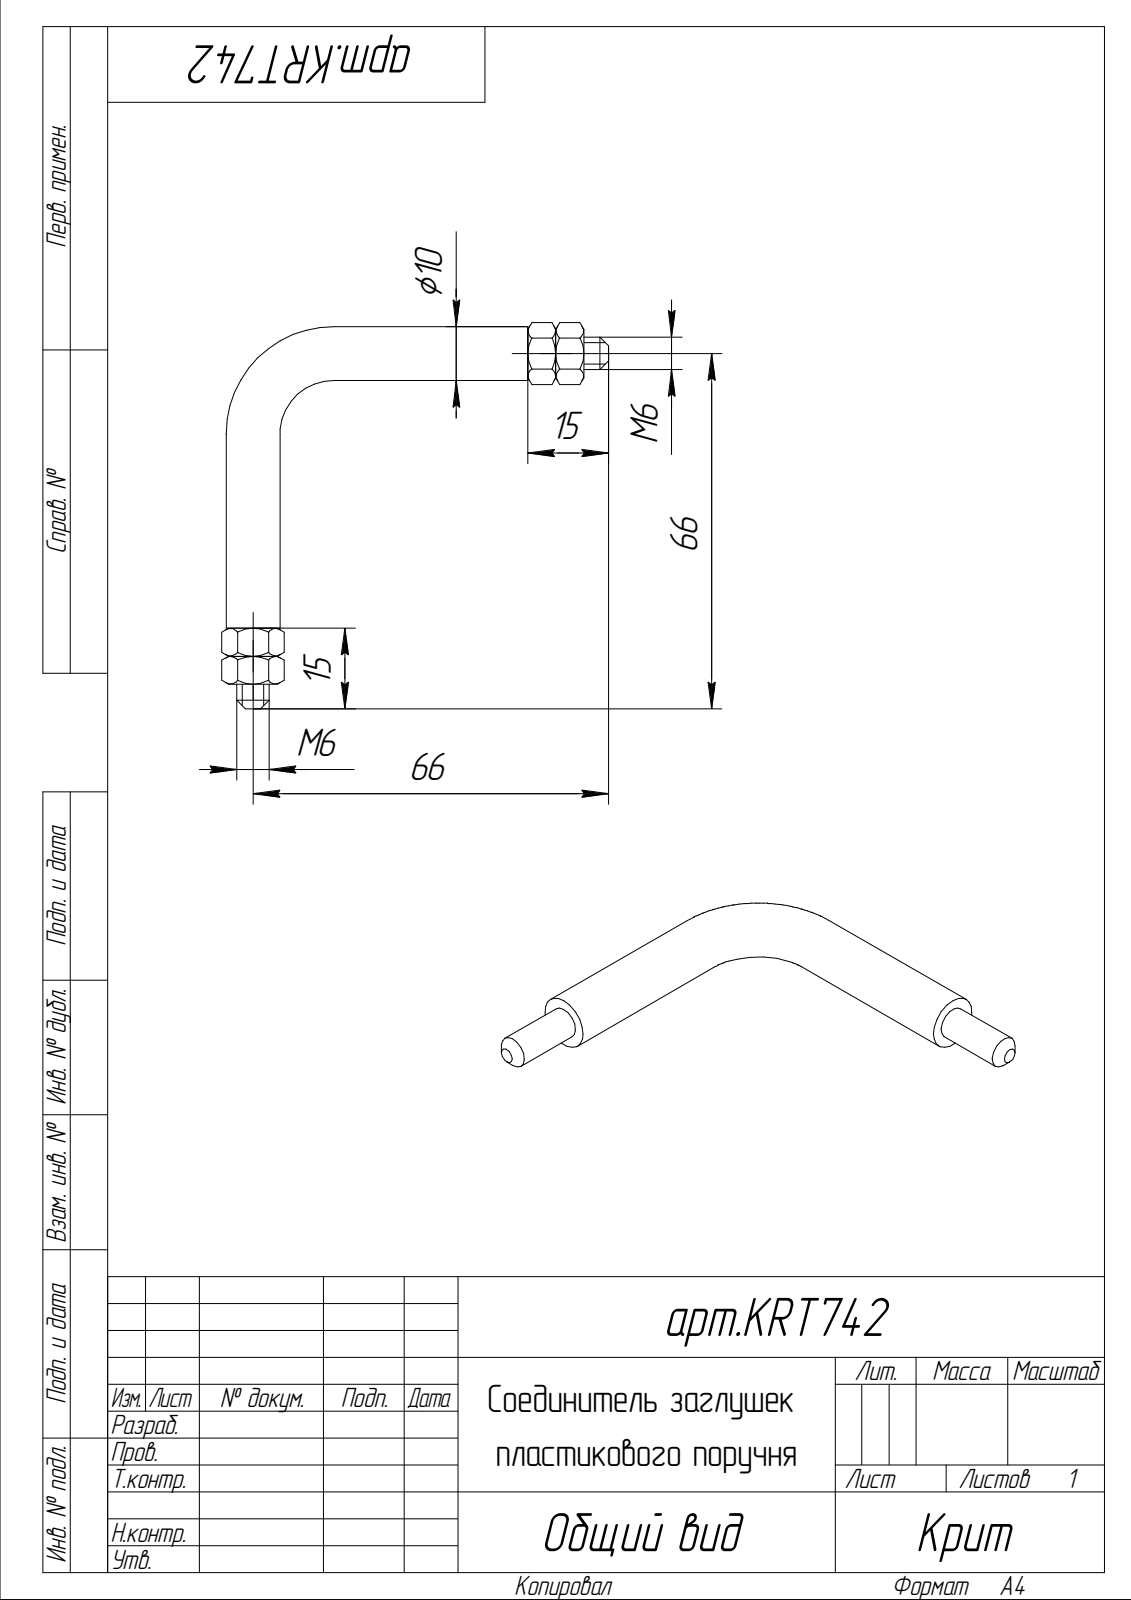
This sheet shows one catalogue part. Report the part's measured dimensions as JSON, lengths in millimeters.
{"part_name": "Соединитель заглушек пластикового поручня", "step_written_by": "ASCON Math Kernel (AUTOMOTIVE_DESIGN)", "units": "millimeters", "bodies": {"solids": 1, "faces": 11, "planar": 4, "cylindrical": 4, "other": 3}, "overall_size": [71, 71, 10], "volume_mm3": 8314, "surface_area_mm2": 3683, "round_bosses_or_shafts": [[10, 2], [6, 2]], "face_to_face_distances": [15]}
